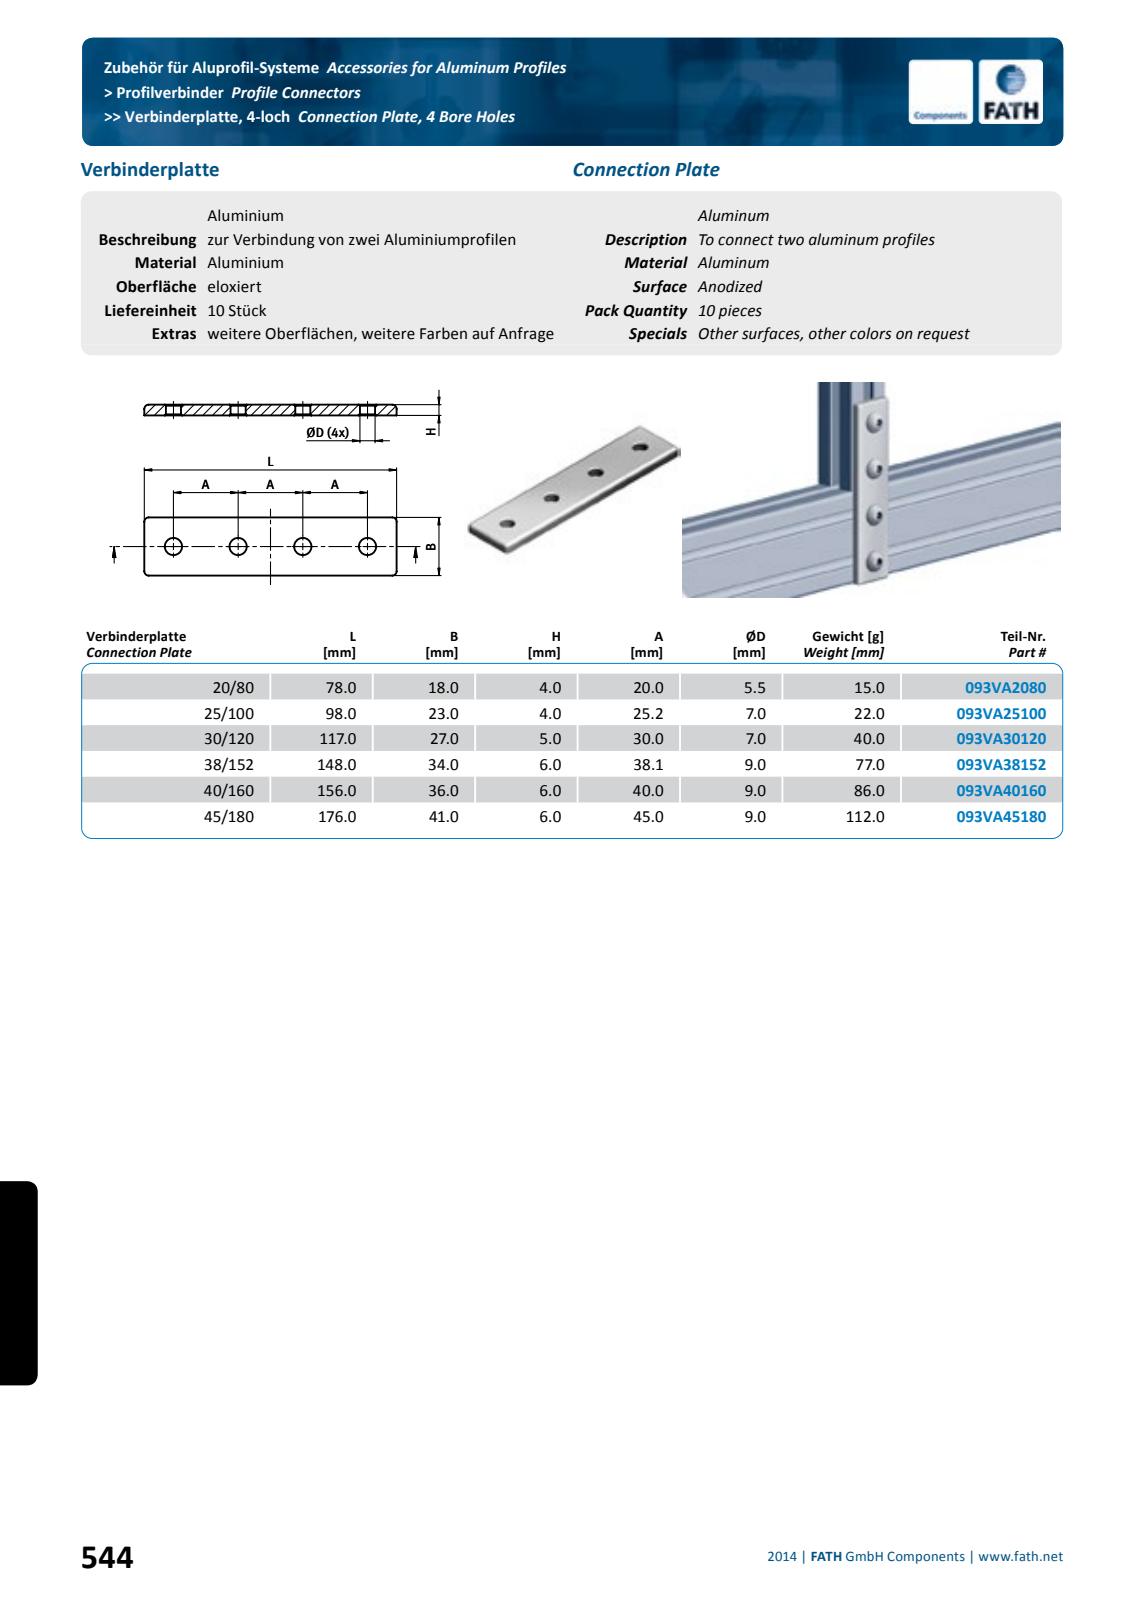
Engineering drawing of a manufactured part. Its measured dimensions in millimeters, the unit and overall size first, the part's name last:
Units: millimetres
Overall size (bounding box): 176 × 41 × 6
Round holes (diameter × count): ⌀9 ×4
Partial cylindrical surfaces — rounded edges, fillets, slot ends (radius × count): R2 ×8
Main face-to-face distances: 6, 41, 176
Hole centre spacings: 45, 90, 135
Volume: 41 352 mm³ · Surface area: 16 743 mm²
Bodies: 1 solid, 42 faces (6 planar, 16 cylindrical, 20 other)
Part name (STEP PRODUCT): fath_093va45180
STEP written by: Spatial InterOp 3D (automotive_design)
